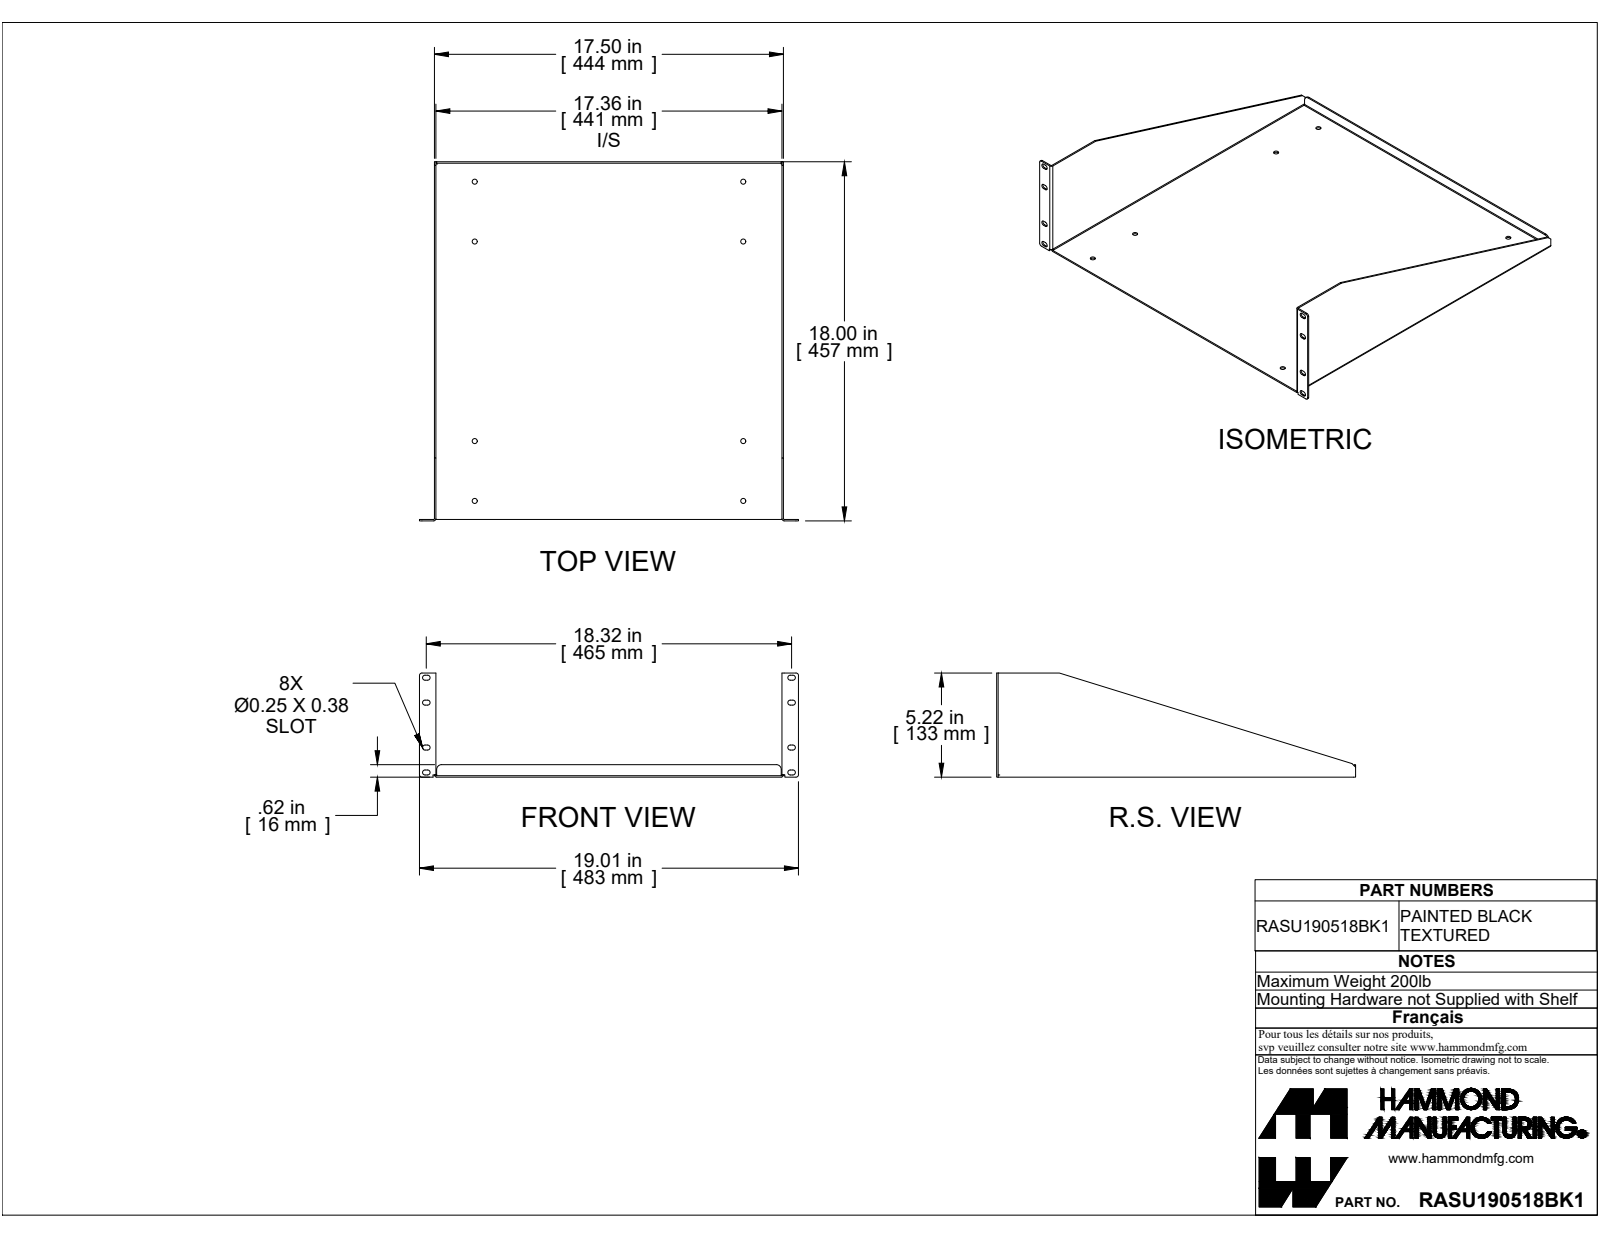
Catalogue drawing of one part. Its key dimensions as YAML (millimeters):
part_name: "RASU190518BK1"
step_written_by: "SolidWorks 2019 (CONFIG_CONTROL_DESIGN)"
units: millimeters
bodies: {solids: 1, faces: 96, planar: 56, cylindrical: 40, other: 0}
overall_size: [482.8, 457.2, 132.5]
volume: 525200
surface_area: 579100
round_holes:
  - {diameter: 6.4, count: 8}
partial_cylinders:
  - {radius: 3.2, count: 20}
  - {radius: 0.9, count: 5}
  - {radius: 2.7, count: 5}
  - {radius: 6.4, count: 2}
face_to_face_distances: [1.8, 442.7, 440.8, 444.5, 453.5, 455.4, 1.8, 455.4, 457.2, 15.9]
hole_center_spacings: [76.2, 330.2, 342.1, 350.5, 475.5, 254, 406.4, 426.1]
